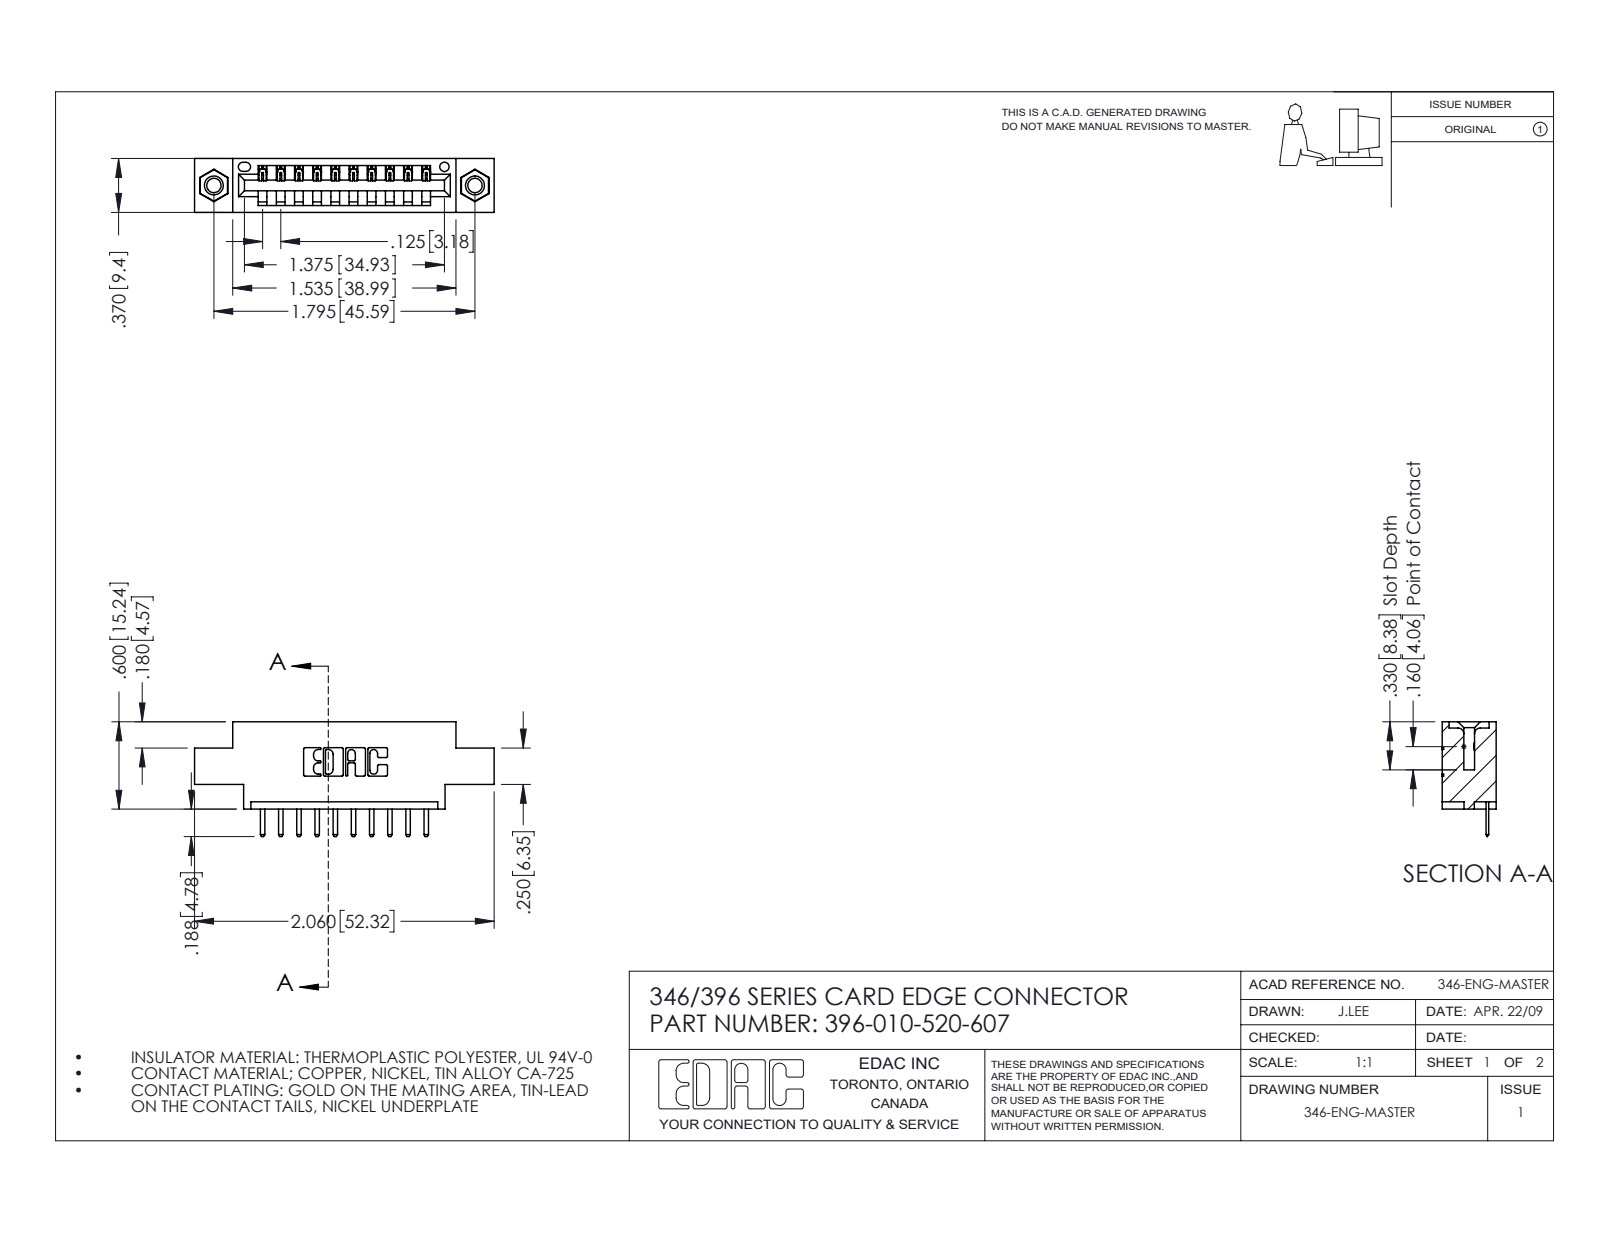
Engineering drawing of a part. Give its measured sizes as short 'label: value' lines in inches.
name: 345-292-001_345-293-120; 346 Part_0.170 Offset - 0.156 Dia-TI; 396-010-520-607; 345-250-001_345-250-005-103
written by: SolidWorks 2016 (CONFIG_CONTROL_DESIGN)
unit: in
bodies: 13 solids, 806 faces (532 planar, 258 cylindrical, 16 other)
size: 2.06 × 0.788 × 0.37
volume: 0.28 in³; area: 8.513 in²
holes: 2× ⌀0.098, 2× ⌀0.125, 2× ⌀0.156, 1× ⌀0.064
bosses: 2× ⌀0.155
rounds: 22× R0.01, 22× R0.01, 20× R0.006, 6× R0.007, 6× R0.031, 3× R0.026, 2× R0.031, 2× R0.04
face distances: 0.25, 0.37, 0.048, 0.322, 0.222, 0.148, 0.1, 0.174, 0.072, 0.298
hole spacings: 0.246, 1.59, 1.795
